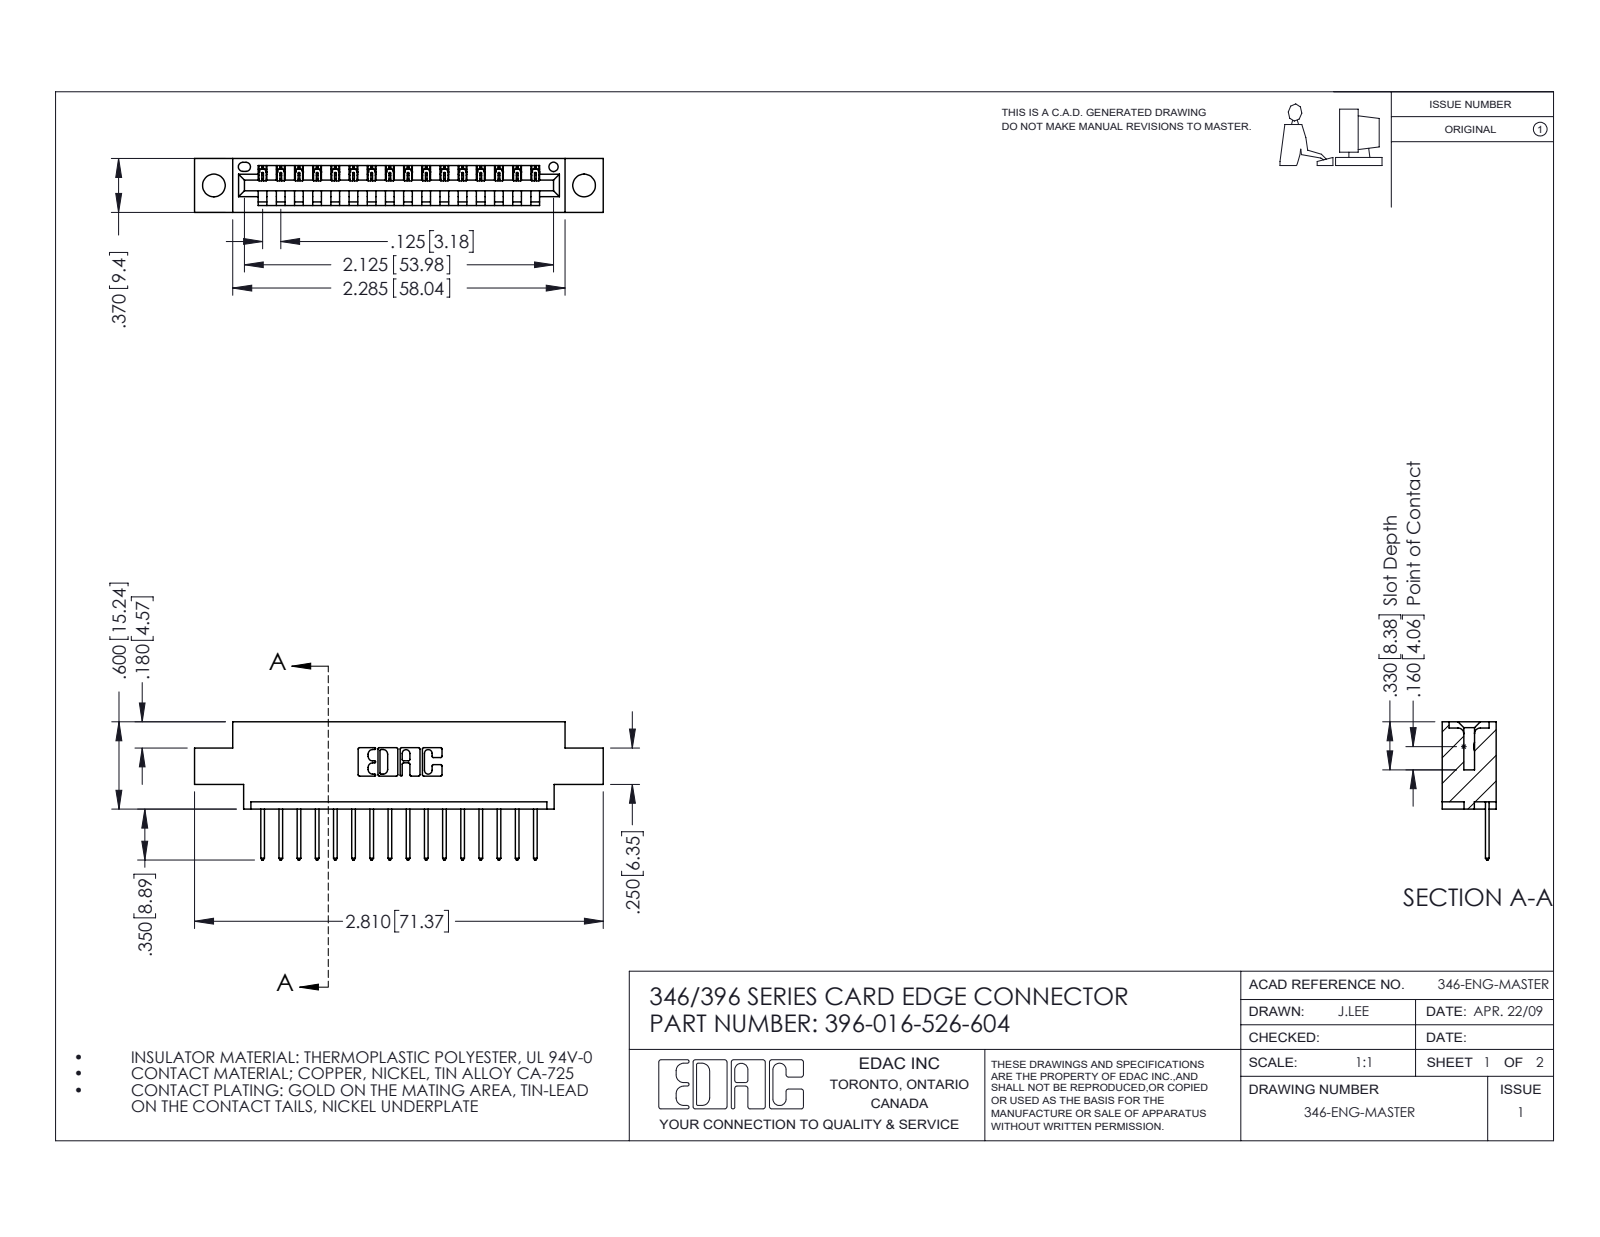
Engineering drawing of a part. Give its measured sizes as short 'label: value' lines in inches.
name: 396-016-526-604; 345-292-001_345-293-126; 346 Part_0.170 Offset - 0.156 Dia-TH
written by: SolidWorks 2016 (CONFIG_CONTROL_DESIGN)
unit: in
bodies: 17 solids, 1054 faces (720 planar, 334 cylindrical, 0 other)
size: 2.81 × 0.95 × 0.37
volume: 0.39 in³; area: 11.88 in²
holes: 2× ⌀0.156, 1× ⌀0.064
rounds: 32× R0.006, 32× R0.01, 22× R0.01, 6× R0.007, 6× R0.031, 3× R0.026, 2× R0.031, 2× R0.04
face distances: 0.048, 0.322, 0.37, 0.25, 0.072, 0.298, 0.025, 0.148, 0.222, 0.1
hole spacings: 0.246, 2.338, 2.545
